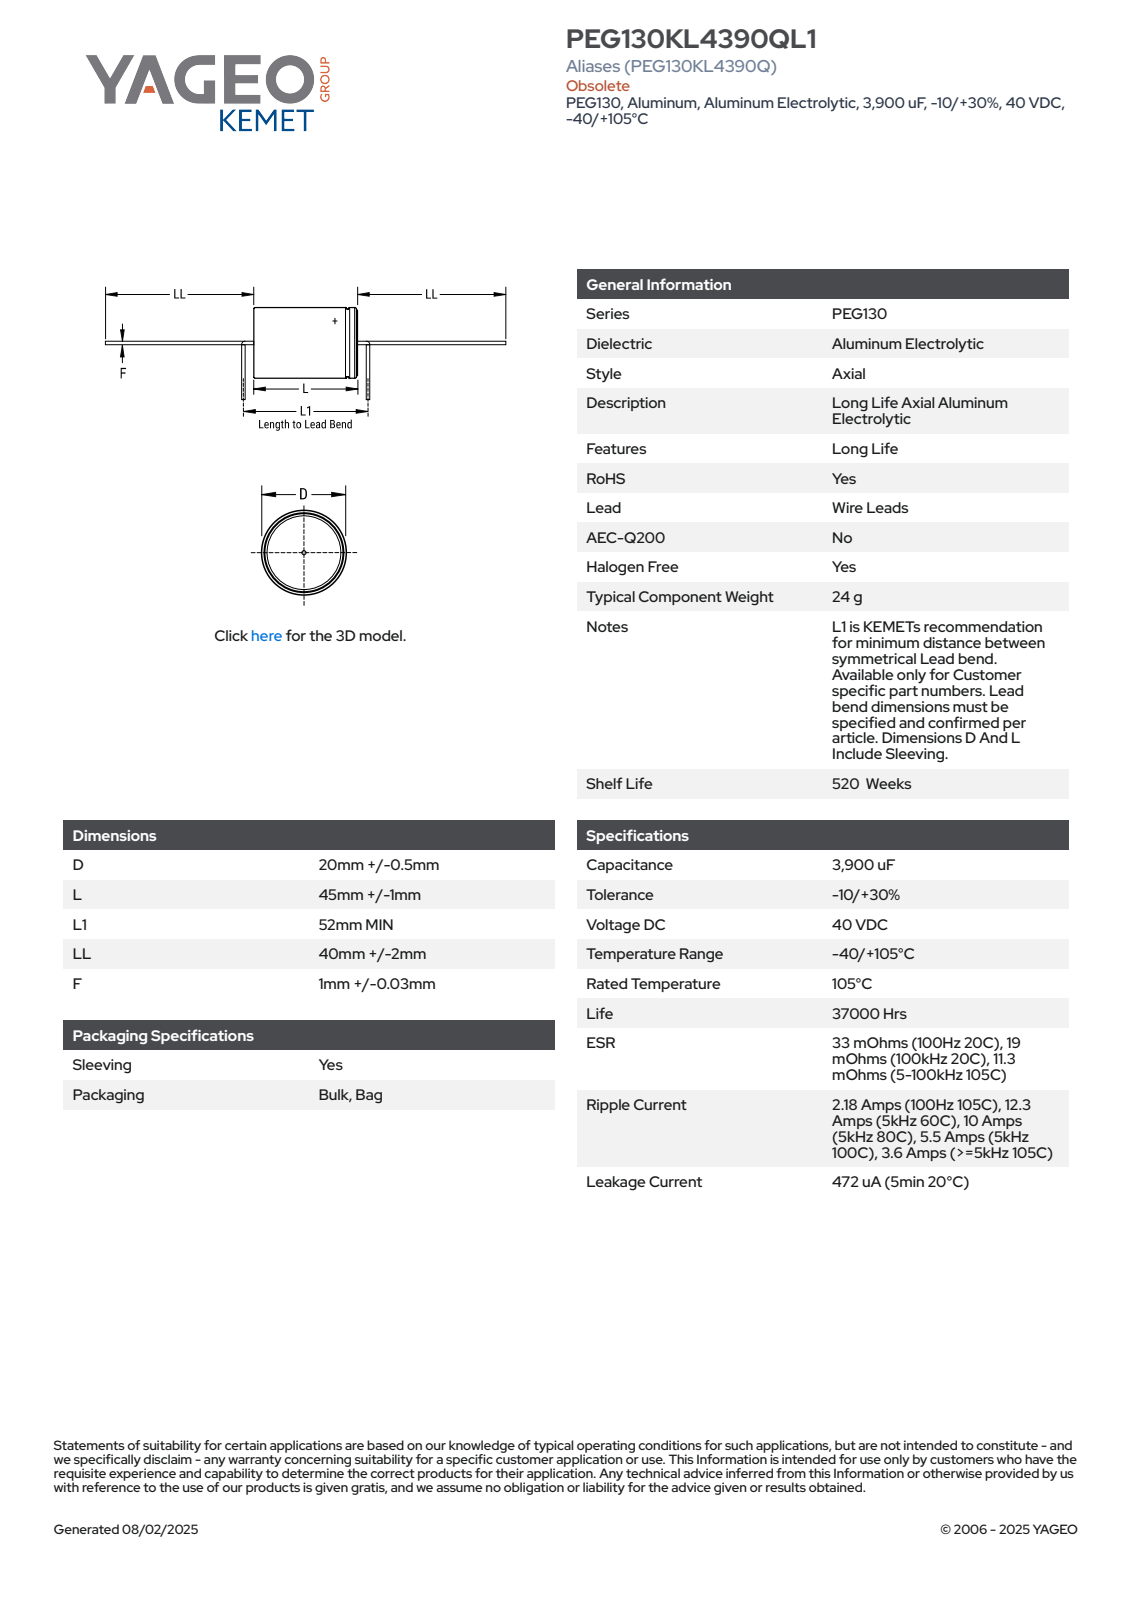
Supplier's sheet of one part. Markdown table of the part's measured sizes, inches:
| quantity | value |
| --- | --- |
| part name | CAA_PEG124_20X46_D20.5L46LL42F1.03 |
| STEP written by | SolidWorks 2021 (AUTOMOTIVE_DESIGN) |
| units | inches |
| bodies | 1 solid, 99 faces (27 planar, 29 cylindrical, 43 other) |
| overall size | 5.118 × 0.807 × 0.807 |
| volume | 0.912 in³ |
| surface area | 6.143 in² |
| round holes (diameter × count) | 0.768 × 1 |
| round bosses / shafts (diameter × count) | 0.807 × 1, 0.787 × 1, 0.041 × 1 |
| partial cylindrical surfaces (radius × count) | 0.403 × 1 |
| main face-to-face distances | 1.772, 1.811, 0.039, 1.654, 3.465, 3.425, 5.118, 1.693 |
